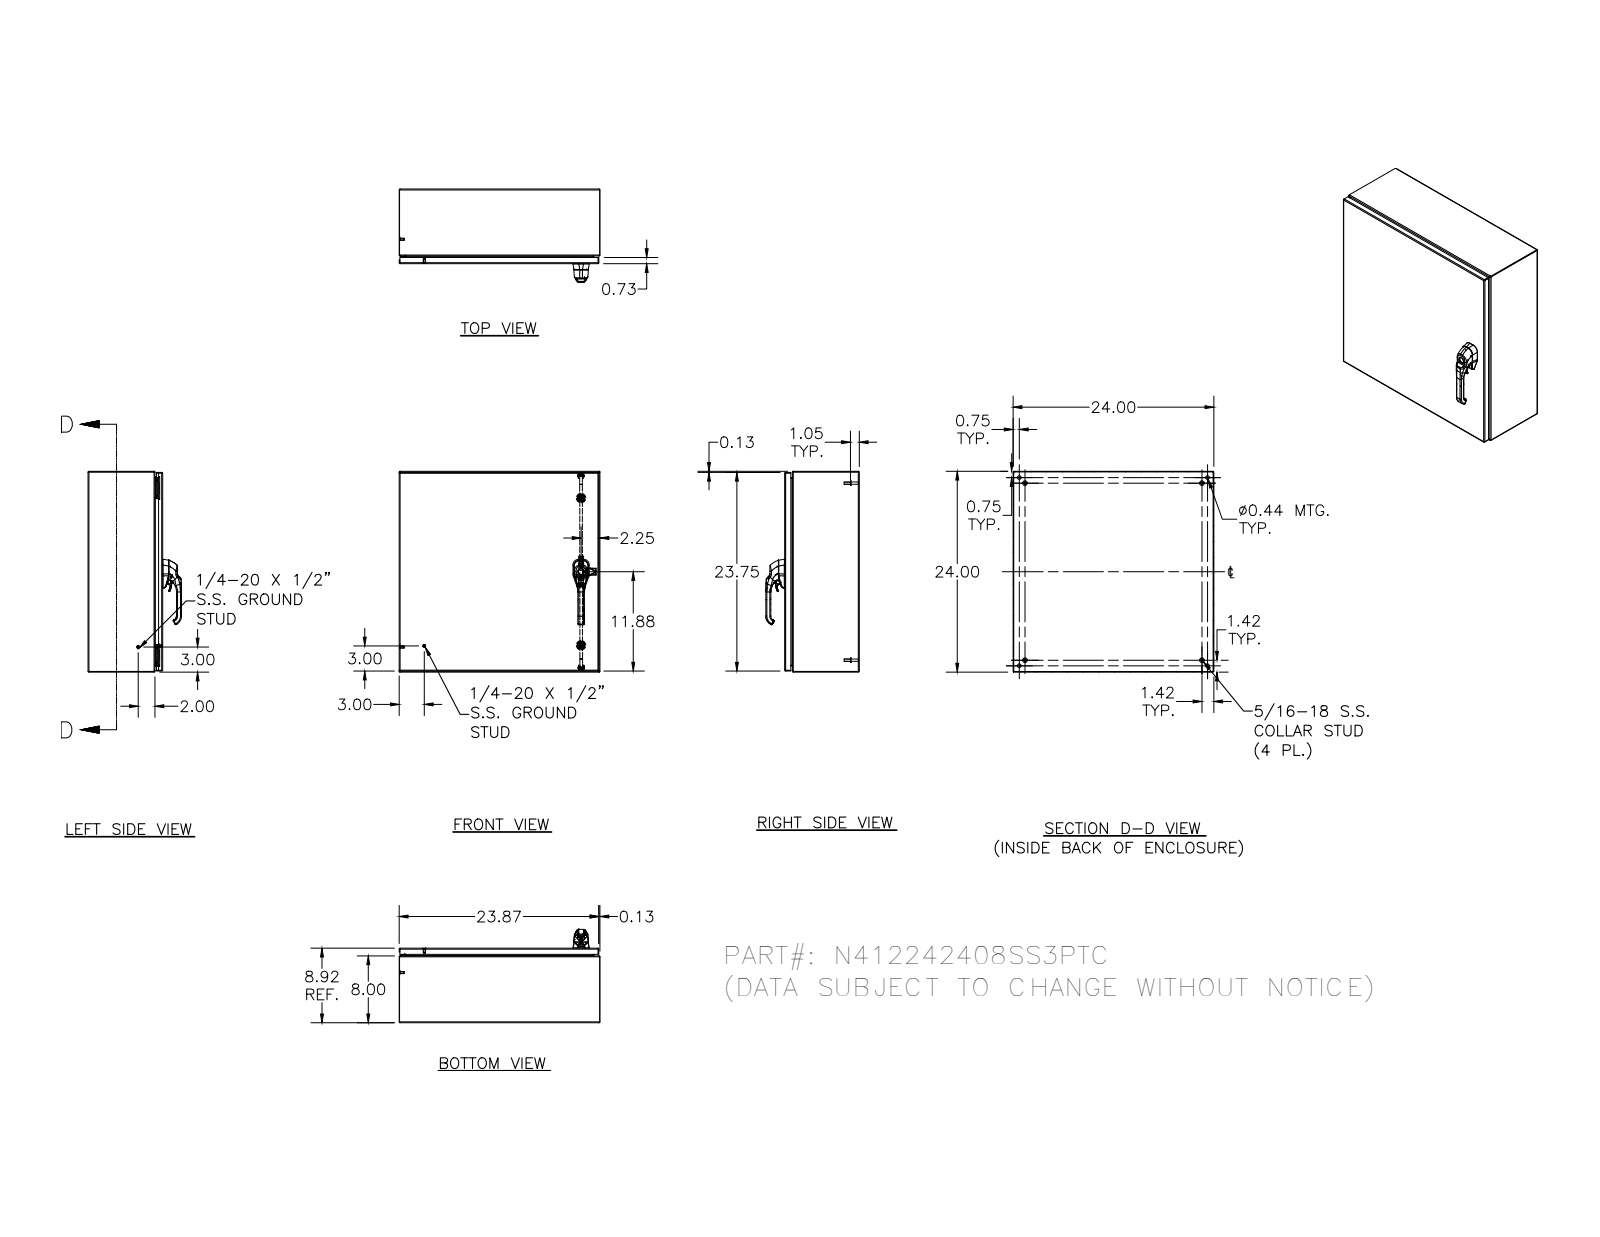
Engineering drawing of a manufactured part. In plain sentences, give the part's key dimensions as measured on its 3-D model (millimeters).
The part is named "N412242408SS3PTC; N412242408SS3PTCBKP; N4122424SS3PTCLID; HFW328176 (+8 more)". Its 3-D file was written by "Autodesk Inventor 2011 (AUTOMOTIVE_DESIGN)". It is 63 solids with 3086 faces: 1046 planar, 1117 cylindrical and 923 other. Overall it measures 609.6 by 609.6 by 283.6 millimeters. Its volume is 2 735 000 cubic millimeters and its surface area 2 830 000 square millimeters. Round holes: 5 of diameter 4.2, 4 of diameter 2.4, 4 of diameter 3.9, 4 of diameter 4.2, 4 of diameter 4.4, 4 of diameter 4.8, 4 of diameter 5, 4 of diameter 11.1, 3 of diameter 5.4, 2 of diameter 2.7, 2 of diameter 4, 2 of diameter 4.1. Round bosses or shafts: 10 of diameter 6.4, 6 of diameter 6, 5 of diameter 15, 4 of diameter 14.3, 4 of diameter 9.1, 4 of diameter 8.1, 4 of diameter 7.9, 4 of diameter 7.6. Partial cylindrical surfaces (rounded edges, fillets, slot ends): 180 of radius 0.5, 101 of radius 0.3, 30 of radius 0.8, 26 of radius 1.3, 23 of radius 3, 21 of radius 0.5, 20 of radius 2.7, 18 of radius 0.4. The main face-to-face distances are 1.9, 224.6, 607.7, 226.5, 222.7, 605.8, 609.6, 201.3, 23.3, 18.8. The hole center spacings are 507.9, 571.5, 580.9, 0.4, 16.8, 41.1, 524.7, 594.8.
